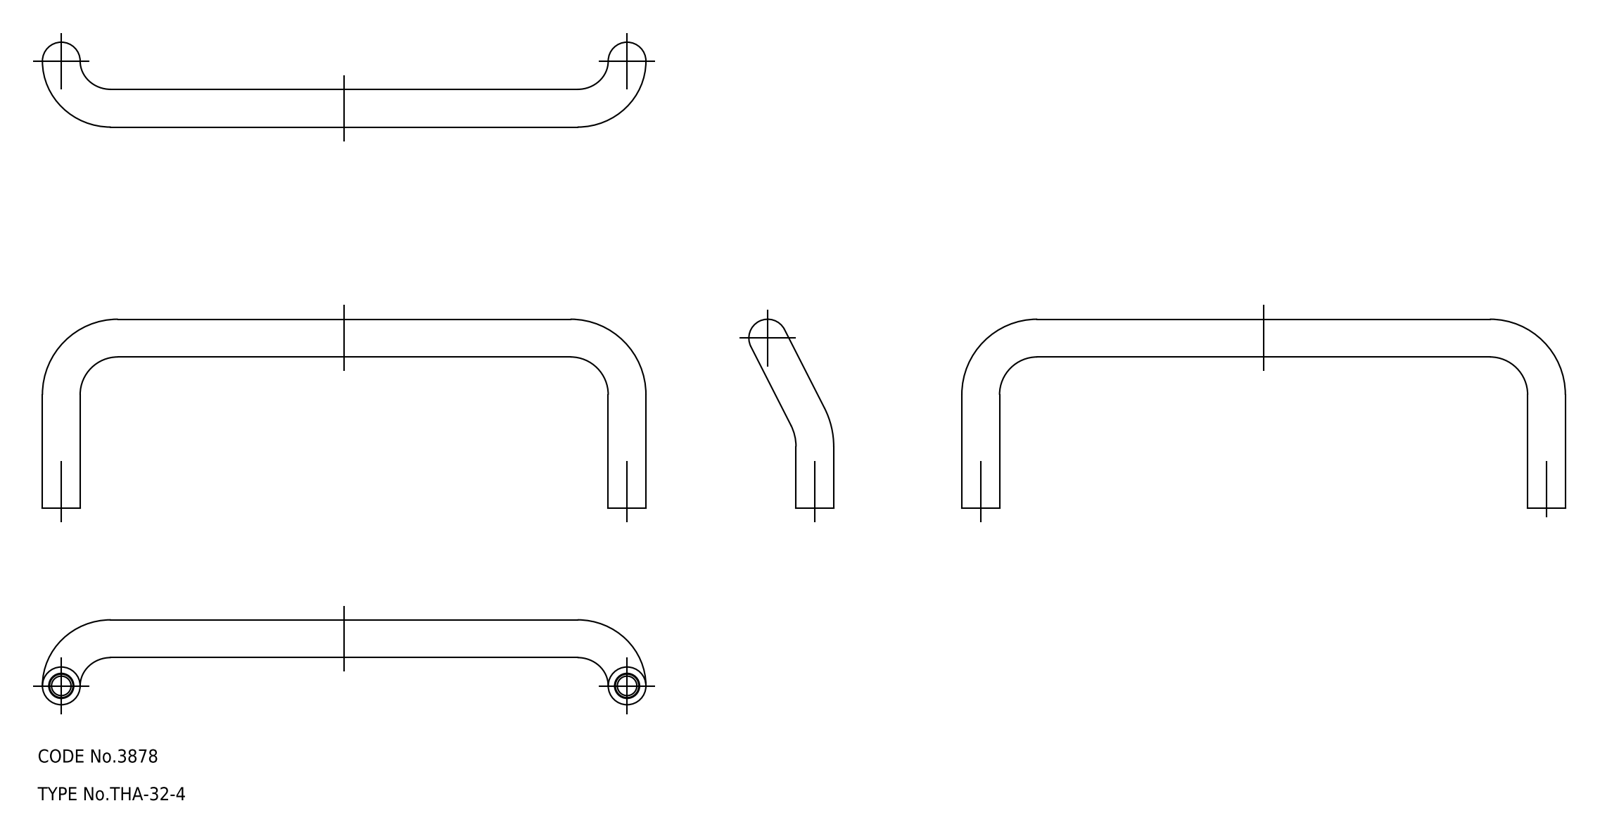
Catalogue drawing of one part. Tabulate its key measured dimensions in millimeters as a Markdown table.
| quantity | value |
| --- | --- |
| STEP written by | spGate 17.5.2 (AUTOMOTIVE_DESIGN) |
| units | millimeters |
| bodies | 1 solid, 30 faces (8 planar, 14 cylindrical, 8 other) |
| overall size | 128 × 40 × 18 |
| volume | 9 164 mm³ |
| surface area | 5 156 mm² |
| round holes (diameter × count) | 5 × 2 |
| round bosses / shafts (diameter × count) | 8 × 5 |
| main face-to-face distances | 10, 7.99 |
| hole center spacings | 120 |
